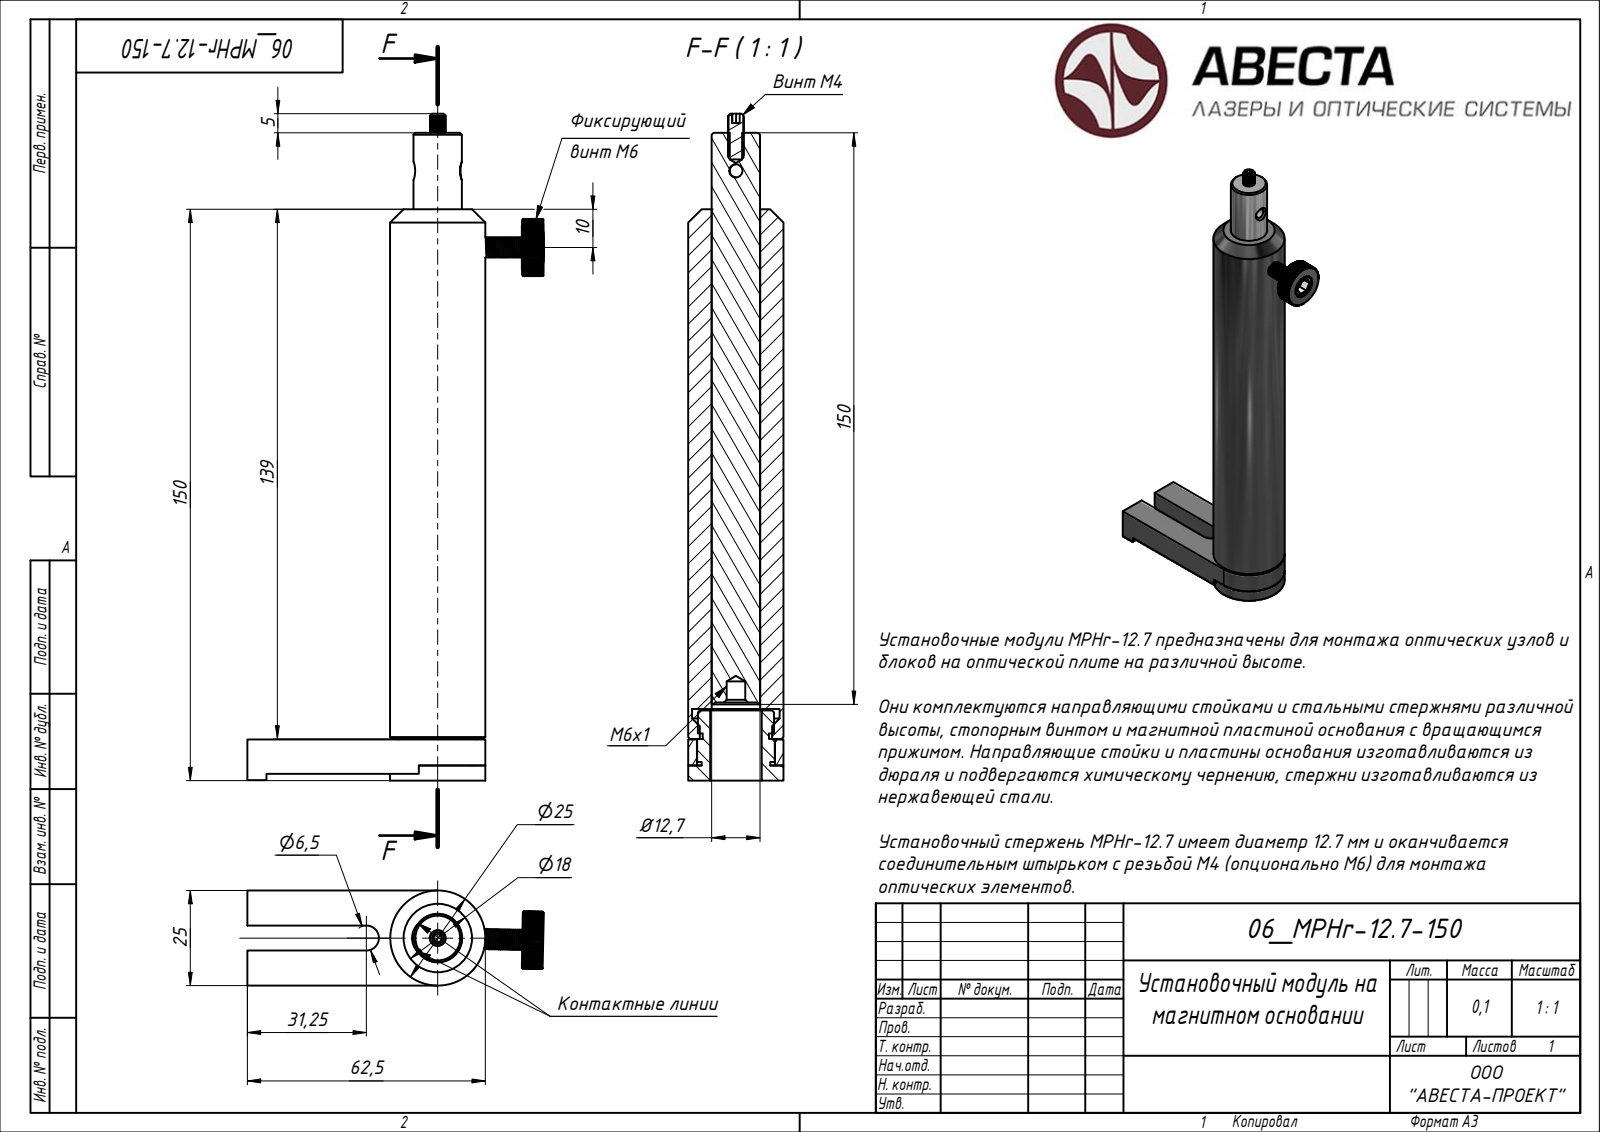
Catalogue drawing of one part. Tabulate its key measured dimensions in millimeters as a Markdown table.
| quantity | value |
| --- | --- |
| STEP written by | ST-DEVELOPER v15 (AUTOMOTIVE_DESIGN) |
| units | millimeters |
| bodies | 48 solids, 3372 faces (1656 planar, 0 cylindrical, 1716 other) |
| overall size | 251.83 × 175.05 × 77.88 |
| volume | 255 929 mm³ |
| surface area | 128 150 mm² |
| main face-to-face distances | 9, 25, 8.99, 9.01, 8.98, 9.25, 15.75, 9.02, 17, 8 |
